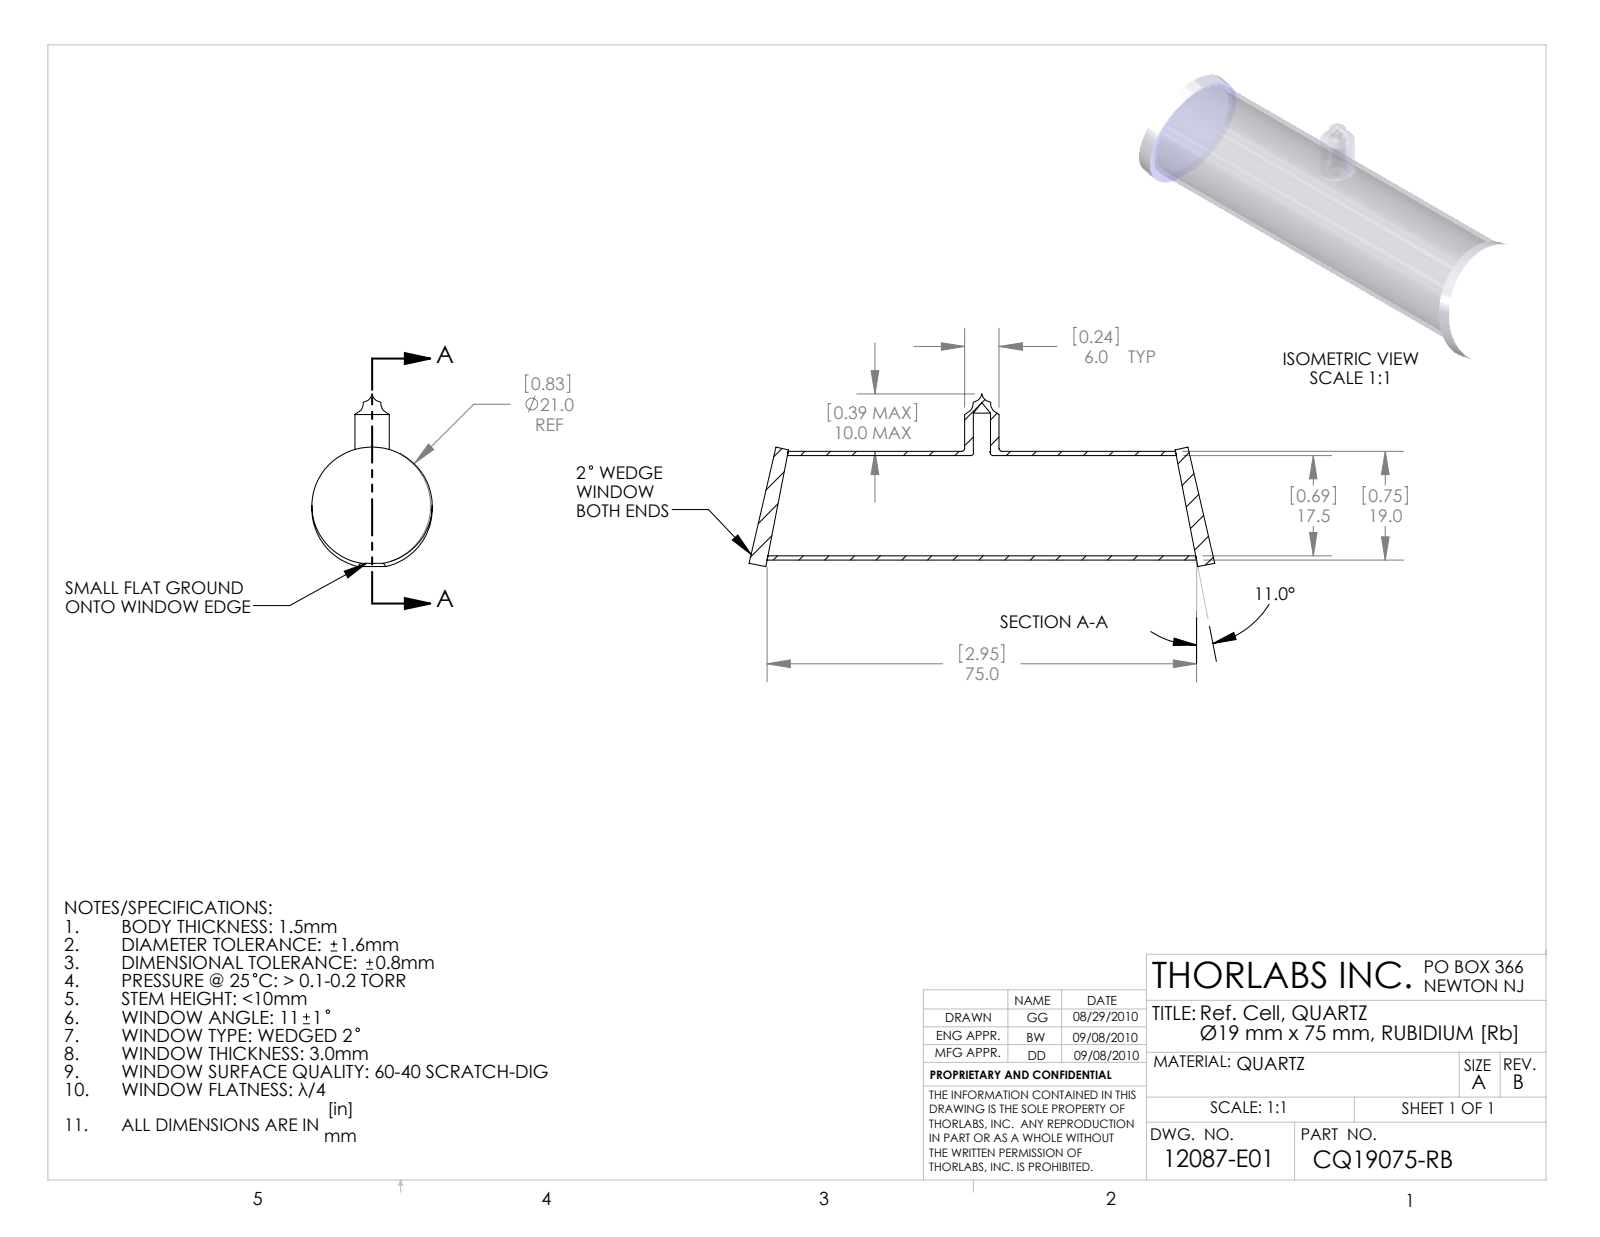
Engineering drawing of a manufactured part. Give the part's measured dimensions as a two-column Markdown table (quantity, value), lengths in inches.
| quantity | value |
| --- | --- |
| part name | 12087-E0W |
| STEP written by | SolidWorks 2009 (AUTOMOTIVE_DESIGN) |
| units | inches |
| bodies | 3 solids, 33 faces (8 planar, 17 cylindrical, 8 other) |
| overall size | 3.201 × 1.186 × 0.827 |
| volume | 0.308 in³ |
| surface area | 15.82 in² |
| round holes (diameter × count) | 0.115 × 1, 0.118 × 1, 0.689 × 1 |
| round bosses / shafts (diameter × count) | 0.827 × 2, 0.748 × 1, 0.236 × 1 |
